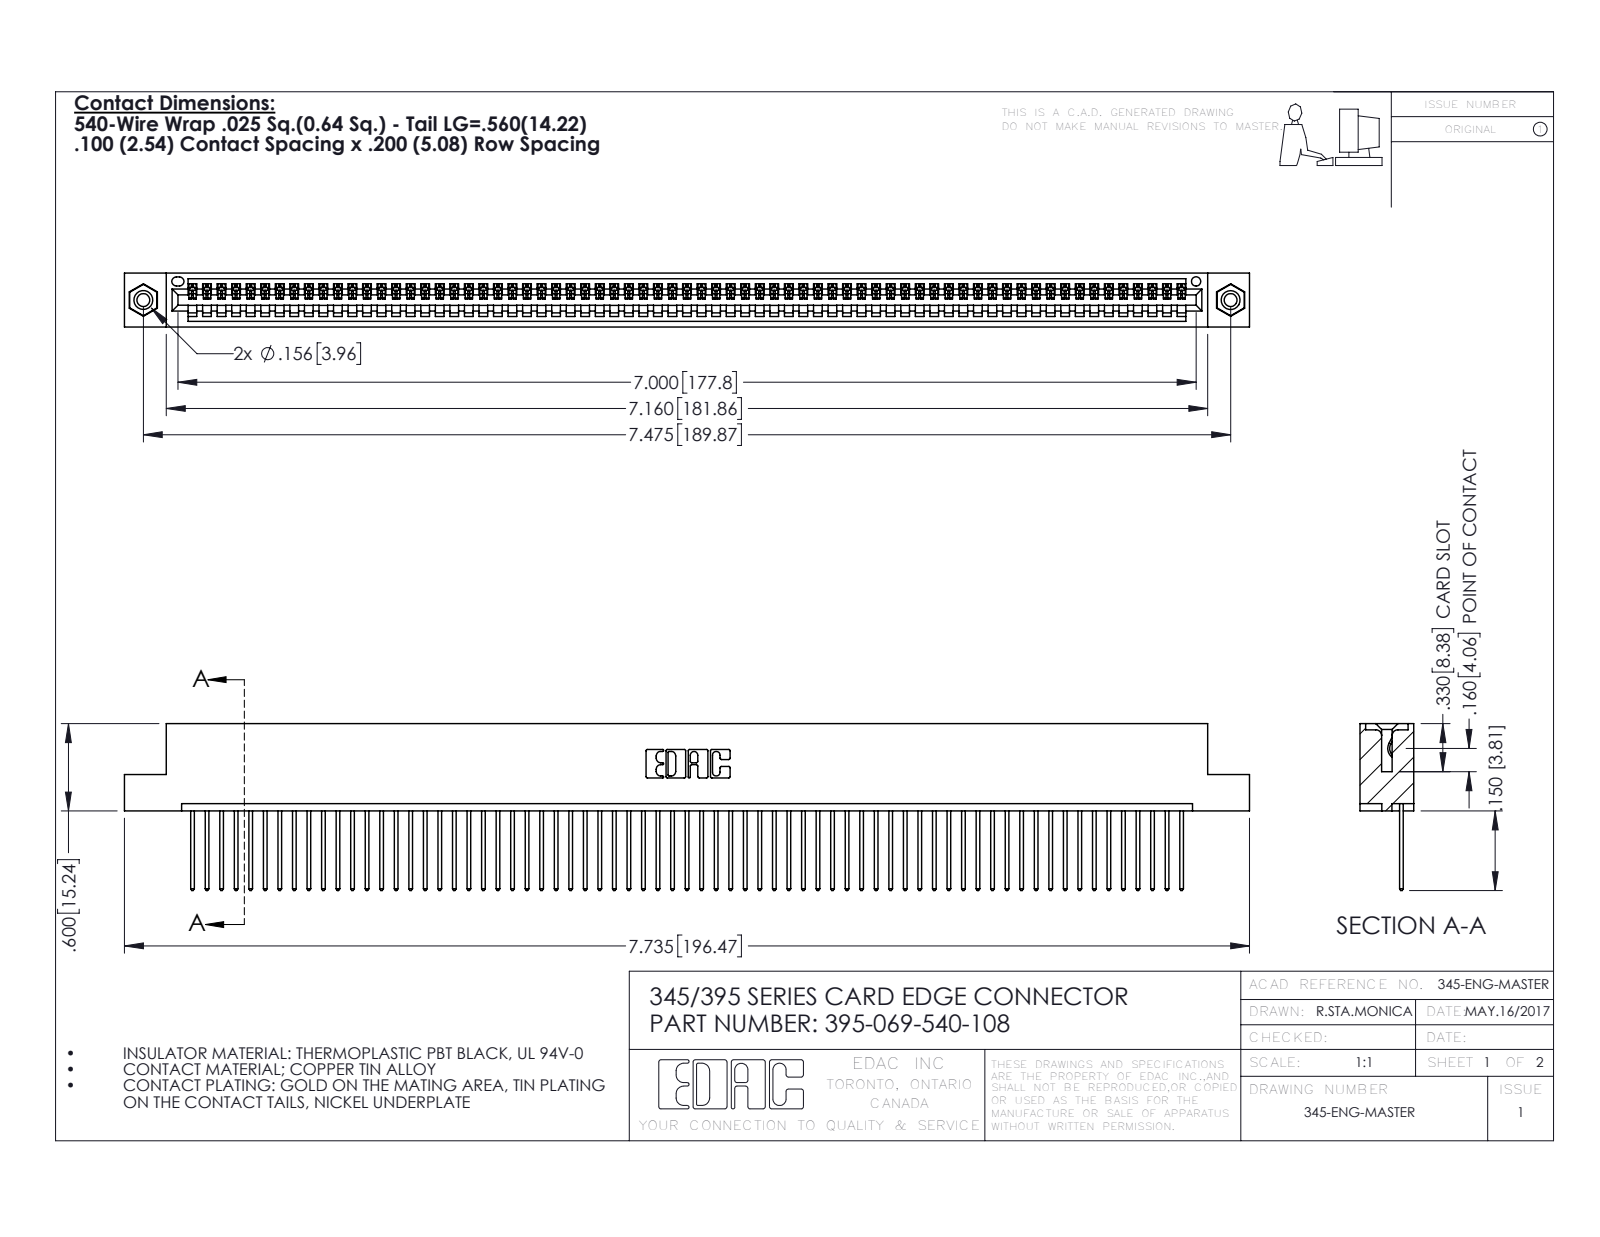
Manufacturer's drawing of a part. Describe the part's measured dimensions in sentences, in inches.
The part is named "345 Part_Flush Mounting Lugs - 0.156 Dia-TI; 345-292-001_345-293-140; 345-250-001_345-250-003-102; 395-069-540-108". Its 3-D file was written by "SolidWorks 2016 (CONFIG_CONTROL_DESIGN)". It is 72 solids with 4188 faces: 2872 planar, 1300 cylindrical and 16 other. Overall it measures 7.735 by 1.147 by 0.37 inches. Its volume is 1.158 cubic inches and its surface area 40.71 square inches. Round holes: 2 of diameter 0.089, 2 of diameter 0.125, 2 of diameter 0.156, 1 of diameter 0.064. Round bosses or shafts: 2 of diameter 0.155. Partial cylindrical surfaces (rounded edges, fillets, slot ends): 138 of radius 0.006, 138 of radius 0.01, 22 of radius 0.01, 6 of radius 0.007, 6 of radius 0.031, 3 of radius 0.026, 2 of radius 0.031, 2 of radius 0.04. The main face-to-face distances are 0.072, 0.298, 0.37, 0.098, 0.272, 0.025, 0.2, 0.225, 0.149, 0.072. The hole center spacings are 0.27, 7.239, 7.475.
